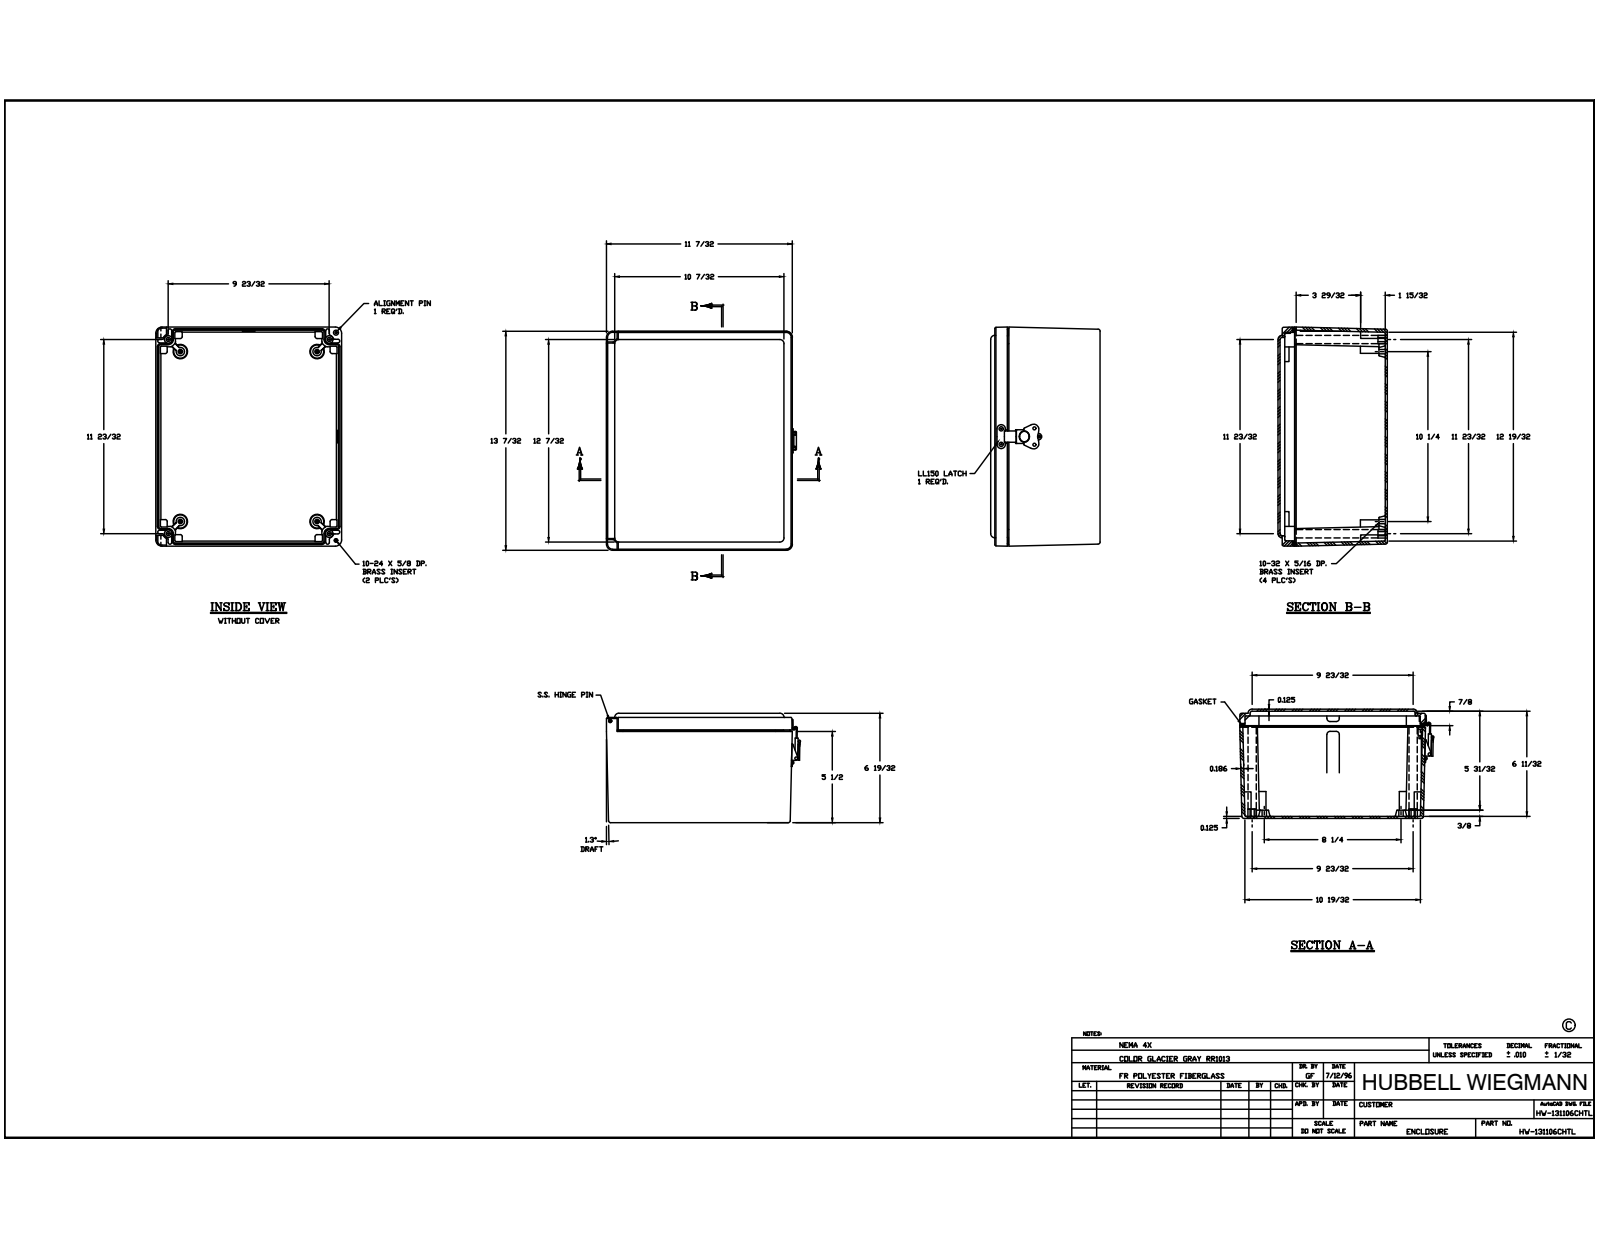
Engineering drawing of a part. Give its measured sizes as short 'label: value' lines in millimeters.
name: WP1311HLLBOX; 0.3125-18 X 0.563 DP BRASS INSERT; 10-32 X0.3125 DP BRASS INSERT; 10-24 X 0.625 DP BRASS INSERT (+8 more)
written by: Autodesk Inventor 2014 (AUTOMOTIVE_DESIGN)
unit: mm
bodies: 30 solids, 1201 faces (427 planar, 417 cylindrical, 357 other)
size: 335.76 × 297.71 × 167.48
volume: 1 799 000 mm³; area: 844 887 mm²
holes: 6× ⌀7.14, 4× ⌀2.64, 4× ⌀3.56, 4× ⌀3.96, 4× ⌀4.76, 4× ⌀7.94, 4× ⌀13.49, 2× ⌀2.44, 2× ⌀3.3, 2× ⌀3.68, 2× ⌀3.97, 2× ⌀4.55
bosses: 2× ⌀9.52, 2× ⌀9.42, 2× ⌀5.94, 2× ⌀3.56, 2× ⌀2.42, 1× ⌀15.24, 1× ⌀7.6, 1× ⌀5.08
rounds: 67× R0.79, 39× R0.51, 39× R3.17, 29× R1.59, 16× R0.25, 10× R6.35, 9× R7.94, 9× R9.53
face distances: 3.17, 164.31, 4.72, 167.48, 161.14, 3.18, 6.35, 161.13, 157.96, 19.05
hole spacings: 12.84, 21.35, 26.38, 228.95, 279.61, 290.76, 308.13, 318.28
